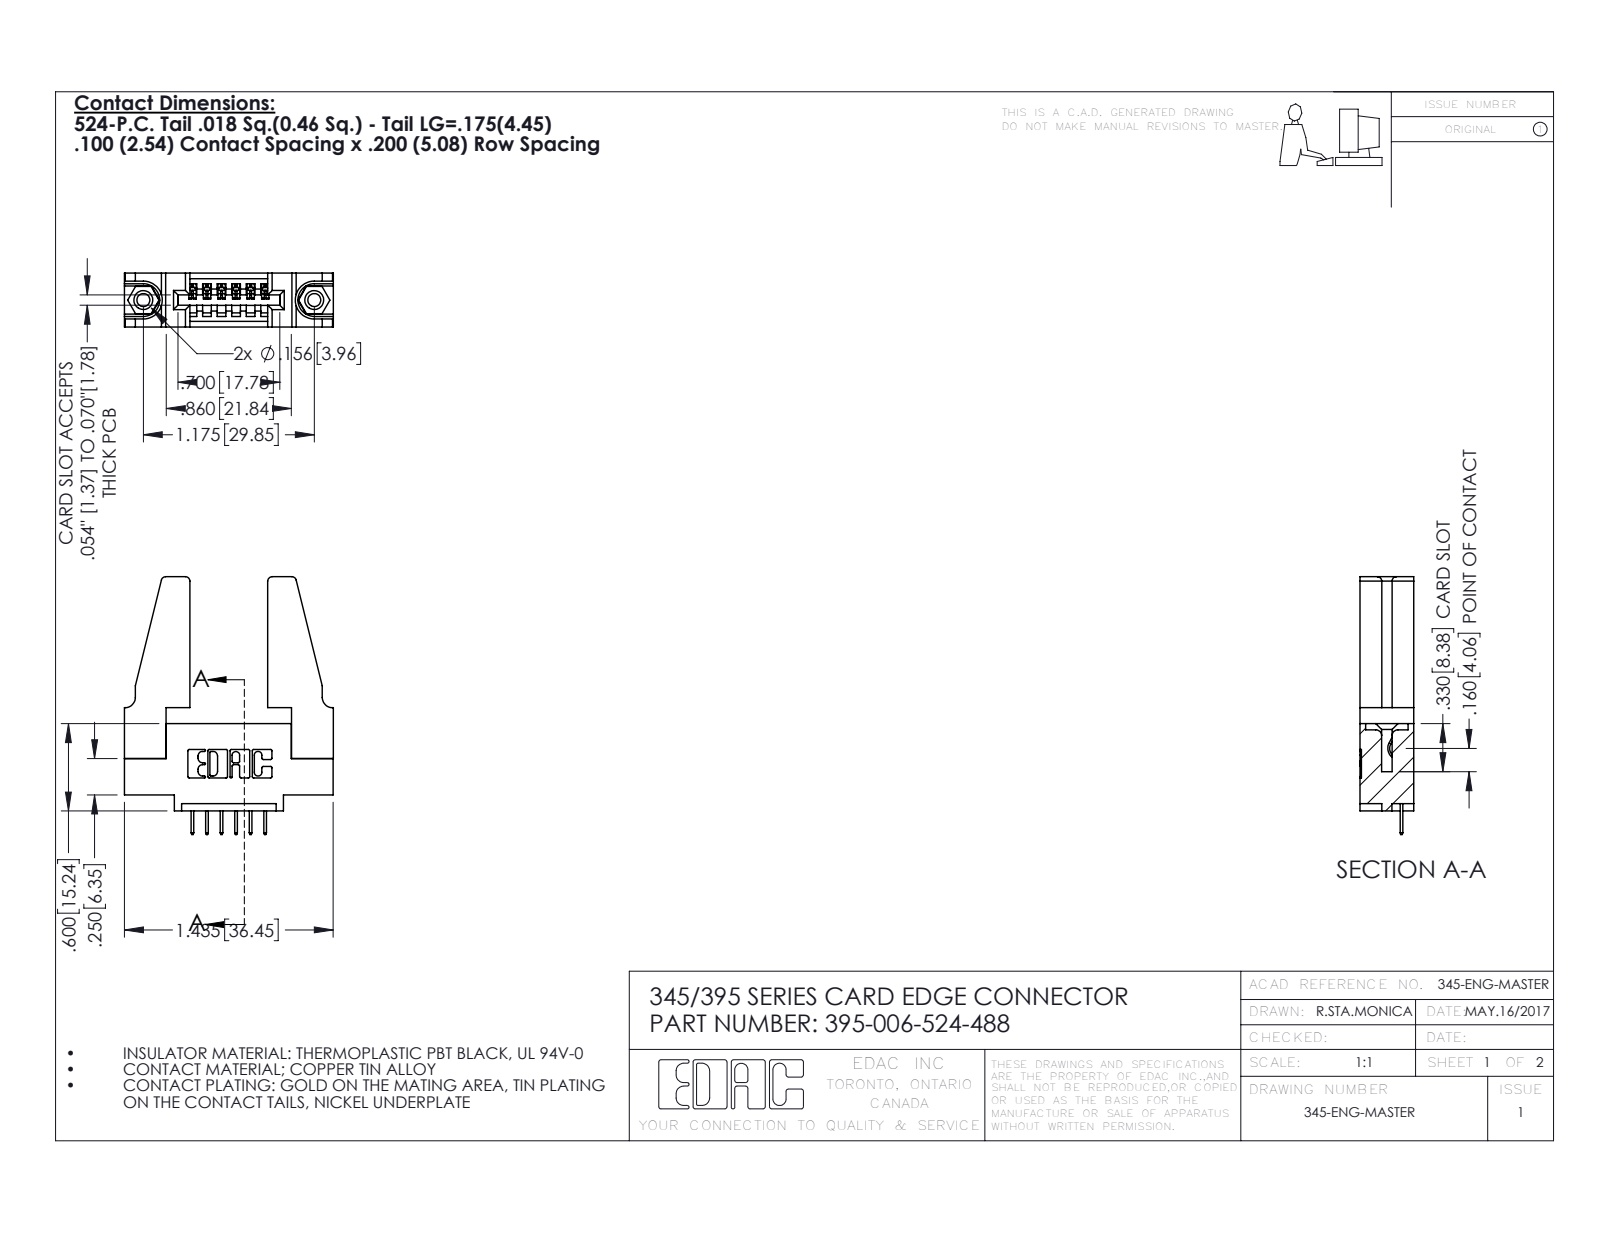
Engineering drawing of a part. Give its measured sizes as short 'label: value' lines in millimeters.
name: 345-220-078_345-220-088; 345-292-001_345-293-124; 345 Part_0.110 Offset - 0.156 Dia-TH; 345-250-001_345-250-001-102 (+1 more)
written by: SolidWorks 2016 (CONFIG_CONTROL_DESIGN)
unit: mm
bodies: 11 solids, 626 faces (432 planar, 178 cylindrical, 16 other)
size: 45 × 36.5 × 9.4
volume: 6 330 mm³; area: 6 729 mm²
holes: 2× ⌀2.3, 2× ⌀3.2, 2× ⌀4, 1× ⌀1.6
bosses: 2× ⌀3.9
rounds: 22× R0.3, 12× R0.2, 8× R0.8, 6× R0.2, 6× R0.8, 3× R0.7, 2× R0.8, 2× R1
face distances: 9.4, 1.8, 7.6, 5.1, 3.8, 3.8, 5.6, 2, 11.4, 17.7
hole spacings: 6.9, 24, 29.8
